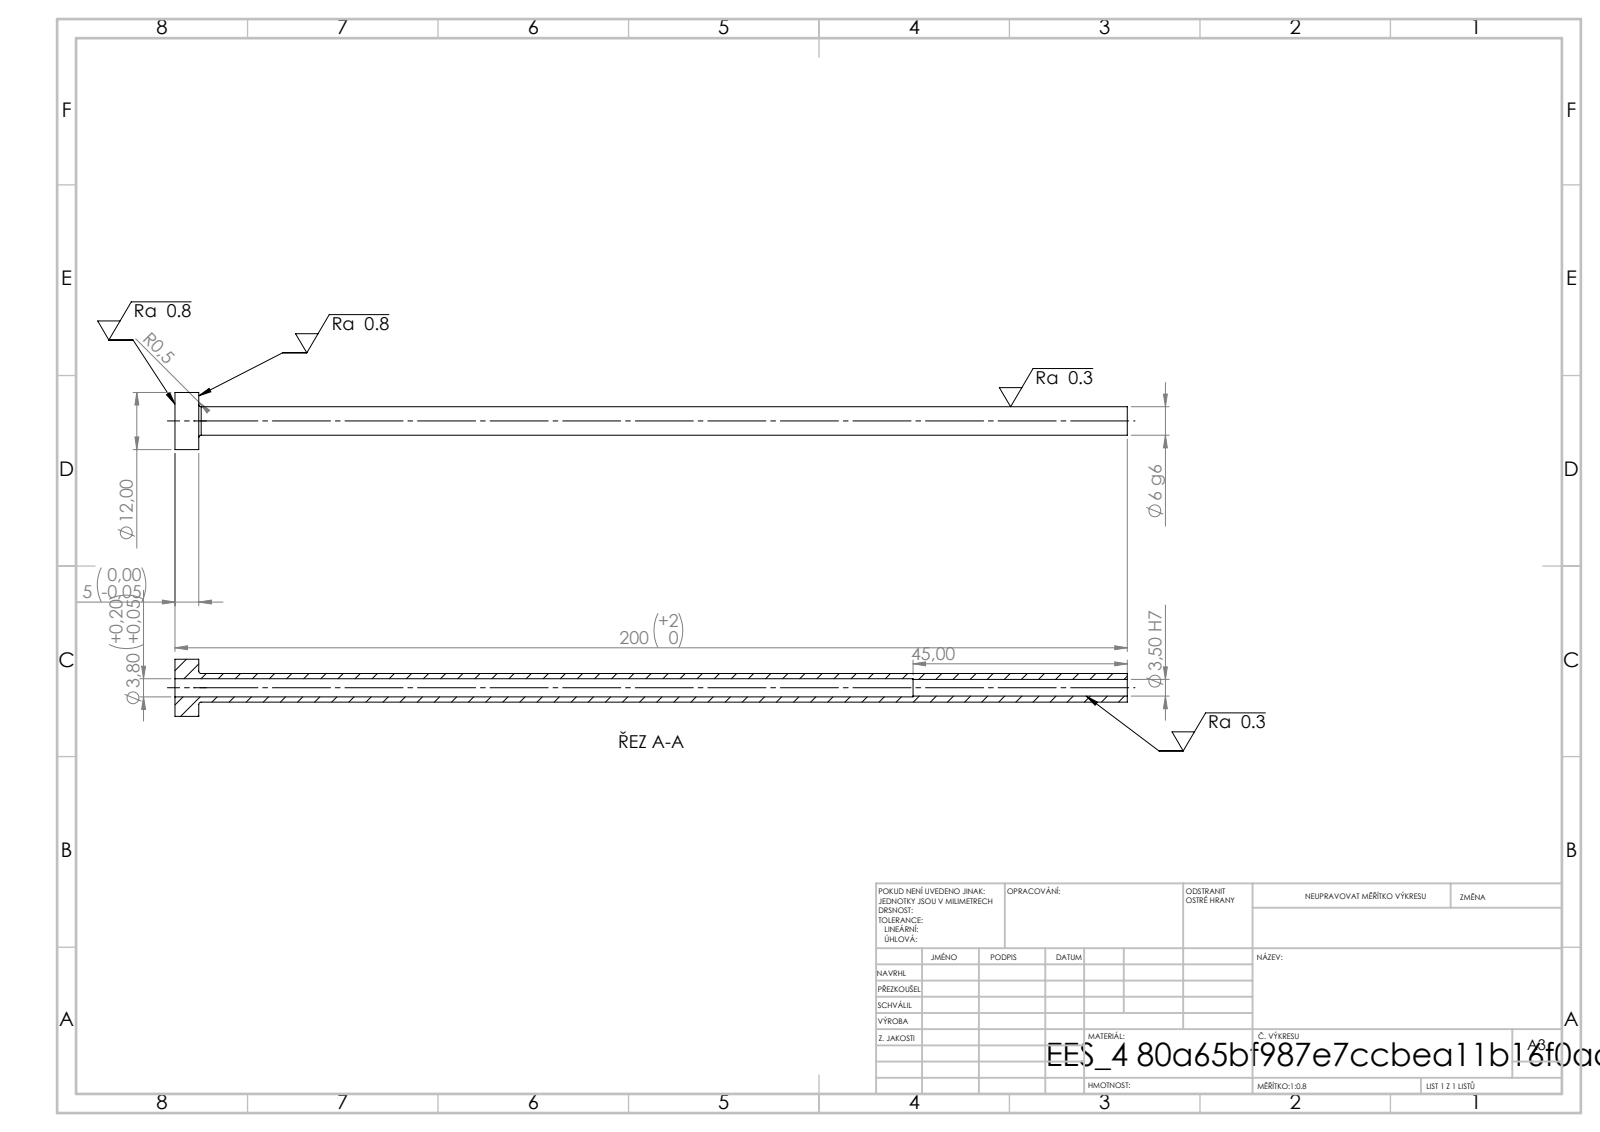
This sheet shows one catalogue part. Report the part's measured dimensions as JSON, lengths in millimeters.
{"step_written_by": "SolidWorks 2019 (CONFIG_CONTROL_DESIGN)", "units": "millimeters", "bodies": {"solids": 1, "faces": 14, "planar": 4, "cylindrical": 8, "other": 2}, "overall_size": [200, 12, 12], "volume_mm3": 3889, "surface_area_mm2": 6412, "round_holes": [[3.5, 1], [3.8, 1]], "round_bosses_or_shafts": [[12, 1], [6, 1]], "face_to_face_distances": [5, 200, 195, 155, 150, 45]}
